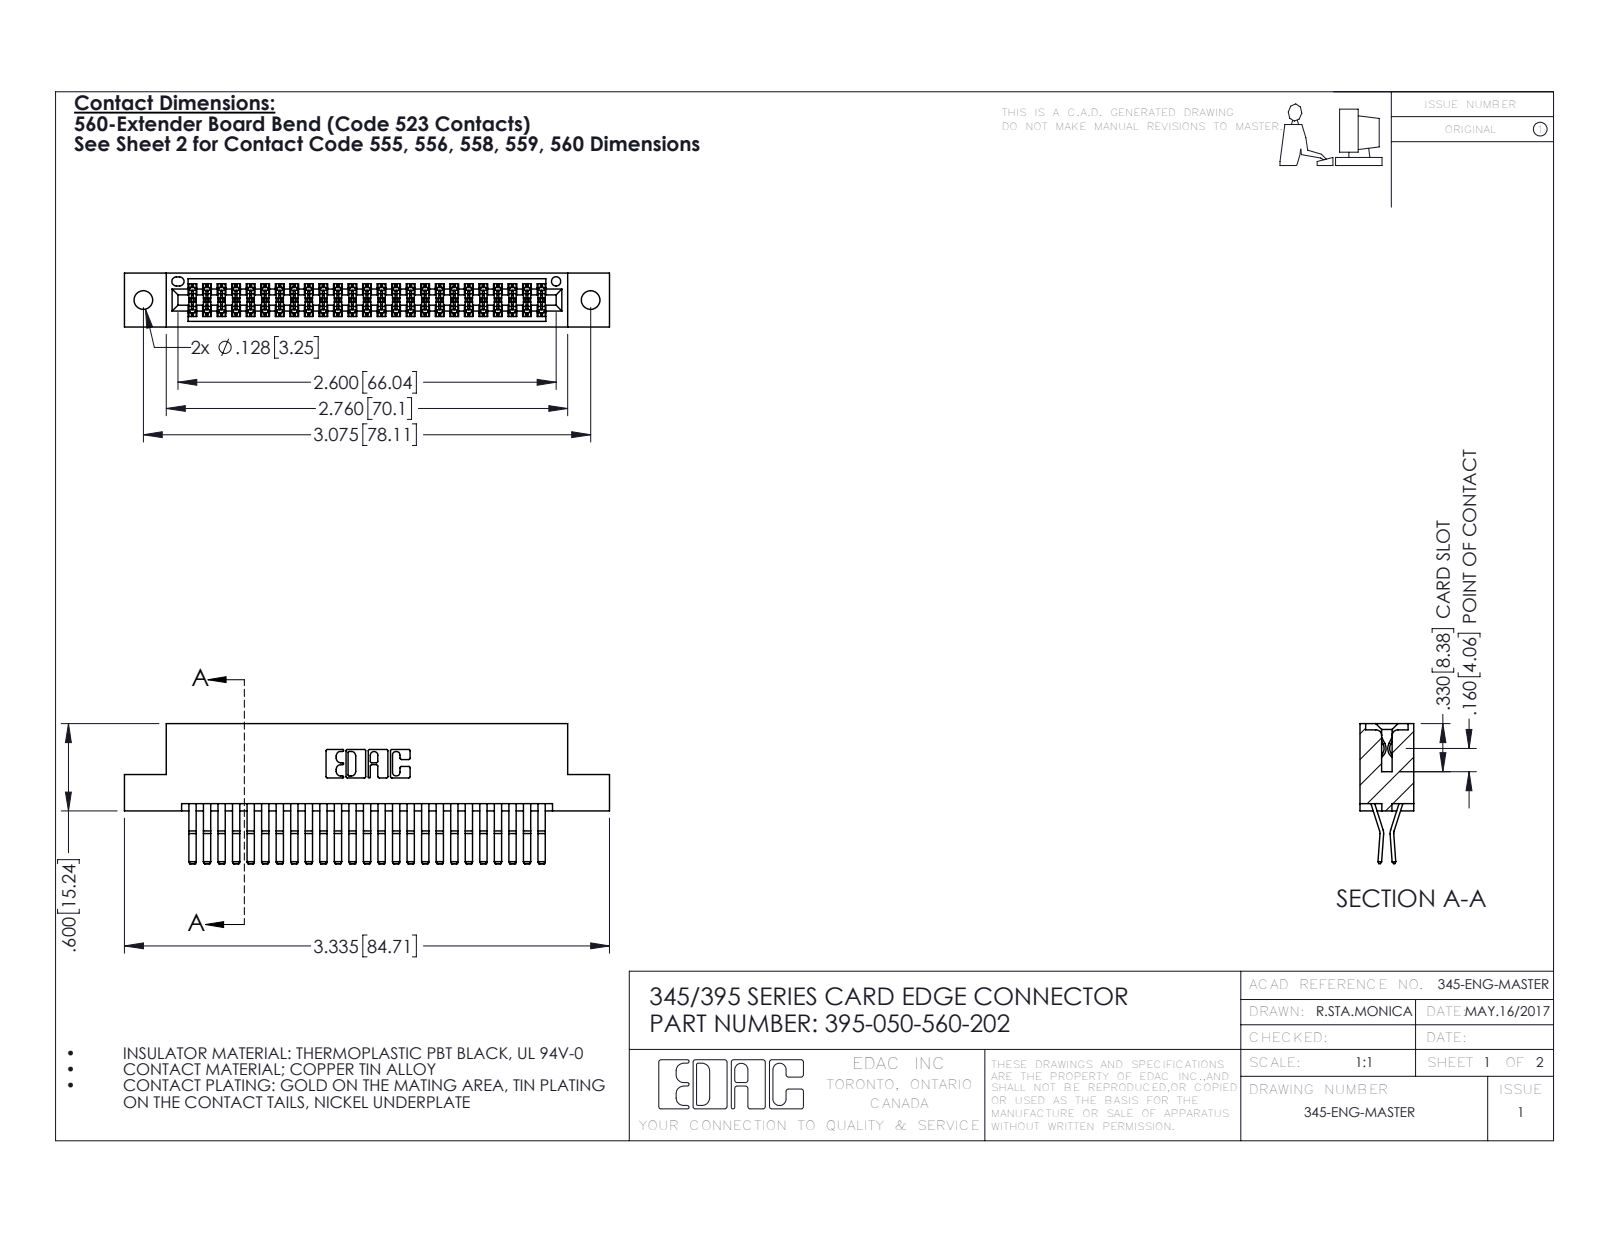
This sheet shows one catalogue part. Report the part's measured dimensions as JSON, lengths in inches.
{"part_name": "345-292-001_560 Tail; 345 Part_Flush Mounting Lugs - 0.128 Dia; 395-050-560-202", "step_written_by": "SolidWorks 2016 (CONFIG_CONTROL_DESIGN)", "units": "inches", "bodies": {"solids": 51, "faces": 2726, "planar": 1730, "cylindrical": 996, "other": 0}, "overall_size": [3.335, 0.962, 0.37], "volume_in3": 0.51, "surface_area_in2": 19.53, "round_holes": [[0.128, 2], [0.064, 1]], "partial_cylinders_radius": [[0.006, 75], [0.01, 22], [0.007, 6], [0.031, 6], [0.026, 3], [0.01, 2], [0.014, 2], [0.019, 2]], "face_to_face_distances": [0.025, 0.298, 0.072, 0.2, 0.37, 0.098, 0.272, 0.225, 0.175, 0.149], "hole_center_spacings": [0.27, 2.84, 3.075]}
